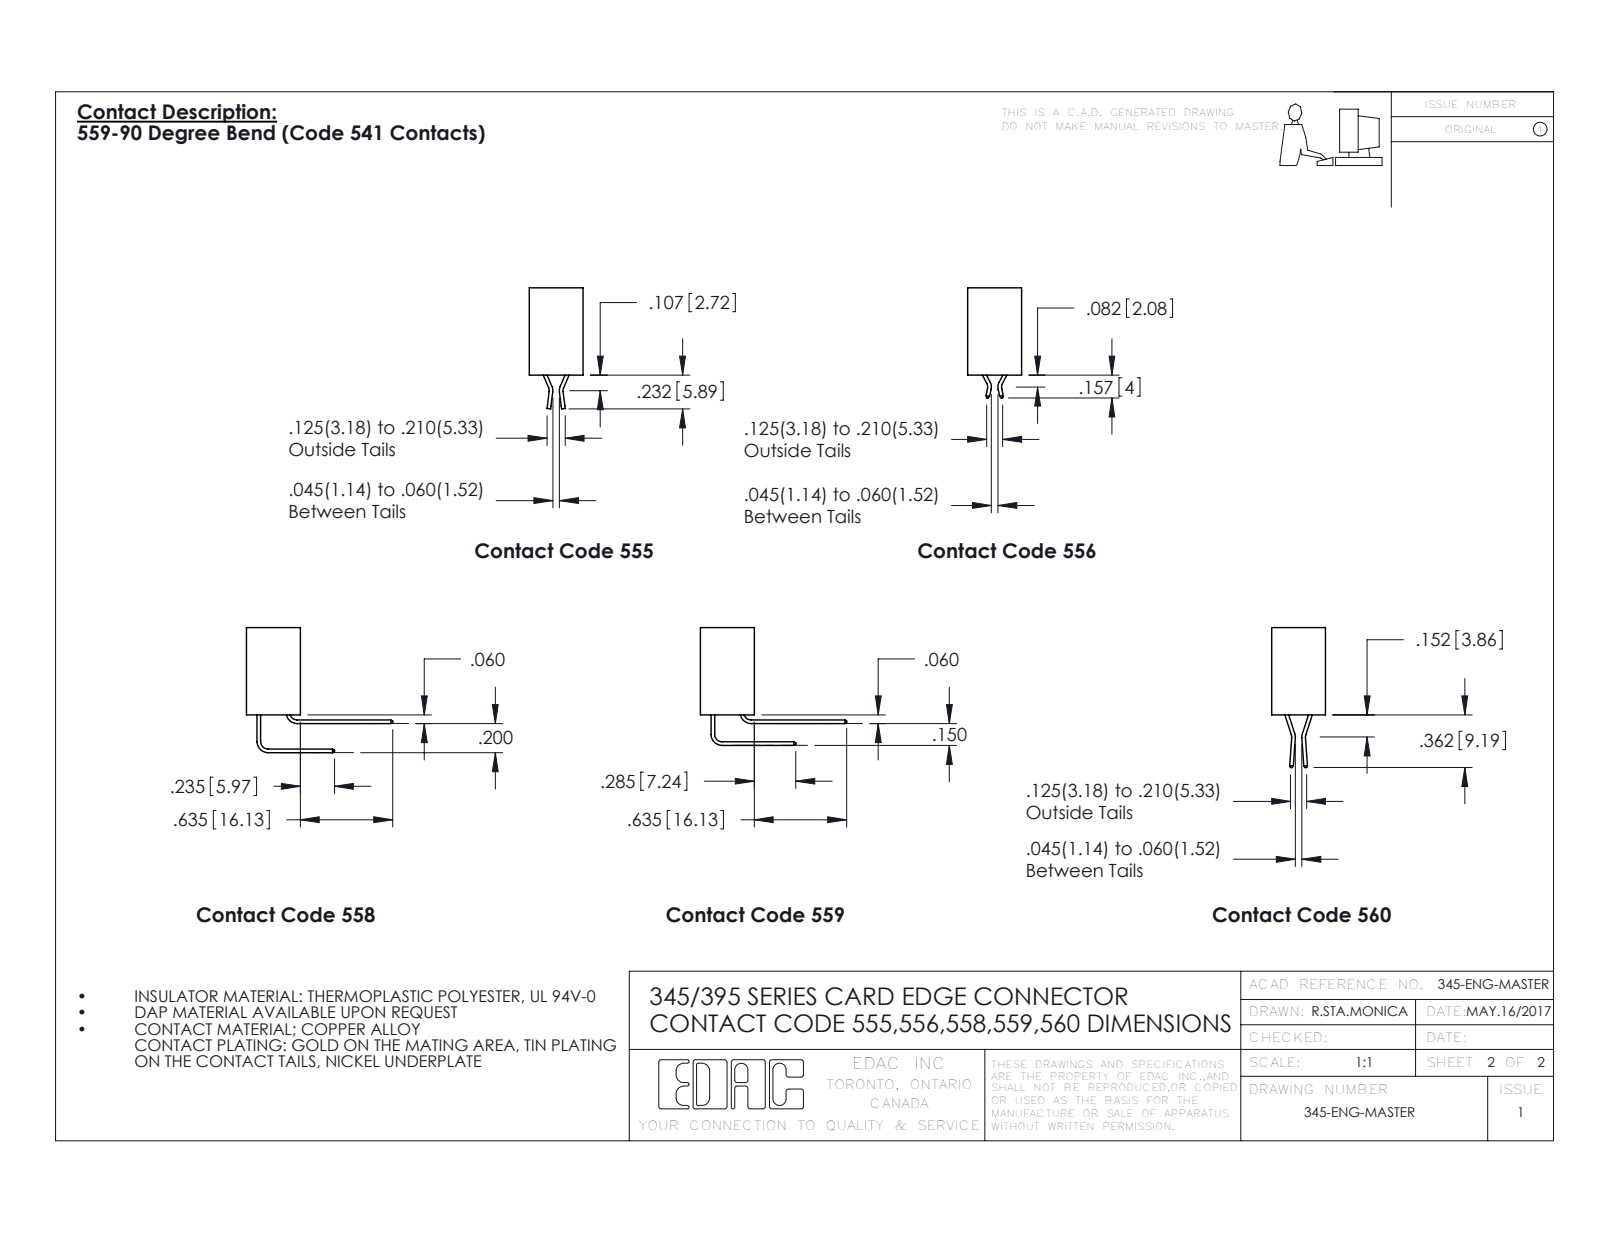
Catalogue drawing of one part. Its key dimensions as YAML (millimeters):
part_name: "345-292-001_556 Tail; 395-054-556-512; 345 Part_0.110 Offset - Side Mount"
step_written_by: "SolidWorks 2016 (CONFIG_CONTROL_DESIGN)"
units: millimeters
bodies: {solids: 55, faces: 3154, planar: 2082, cylindrical: 1072, other: 0}
overall_size: [89.8, 19.2, 9.4]
volume: 8420
surface_area: 12060
round_holes:
  - {diameter: 3.3, count: 2}
  - {diameter: 1.6, count: 1}
partial_cylinders:
  - {radius: 0.2, count: 81}
  - {radius: 0.3, count: 22}
  - {radius: 0.2, count: 6}
  - {radius: 0.8, count: 6}
  - {radius: 0.7, count: 3}
  - {radius: 0.3, count: 2}
  - {radius: 0.4, count: 2}
  - {radius: 0.5, count: 2}
face_to_face_distances: [7.6, 1.8, 9.4, 5.1, 0.6, 2.5, 6.9, 5.7, 4.4, 3.8]
hole_center_spacings: [83.2]
